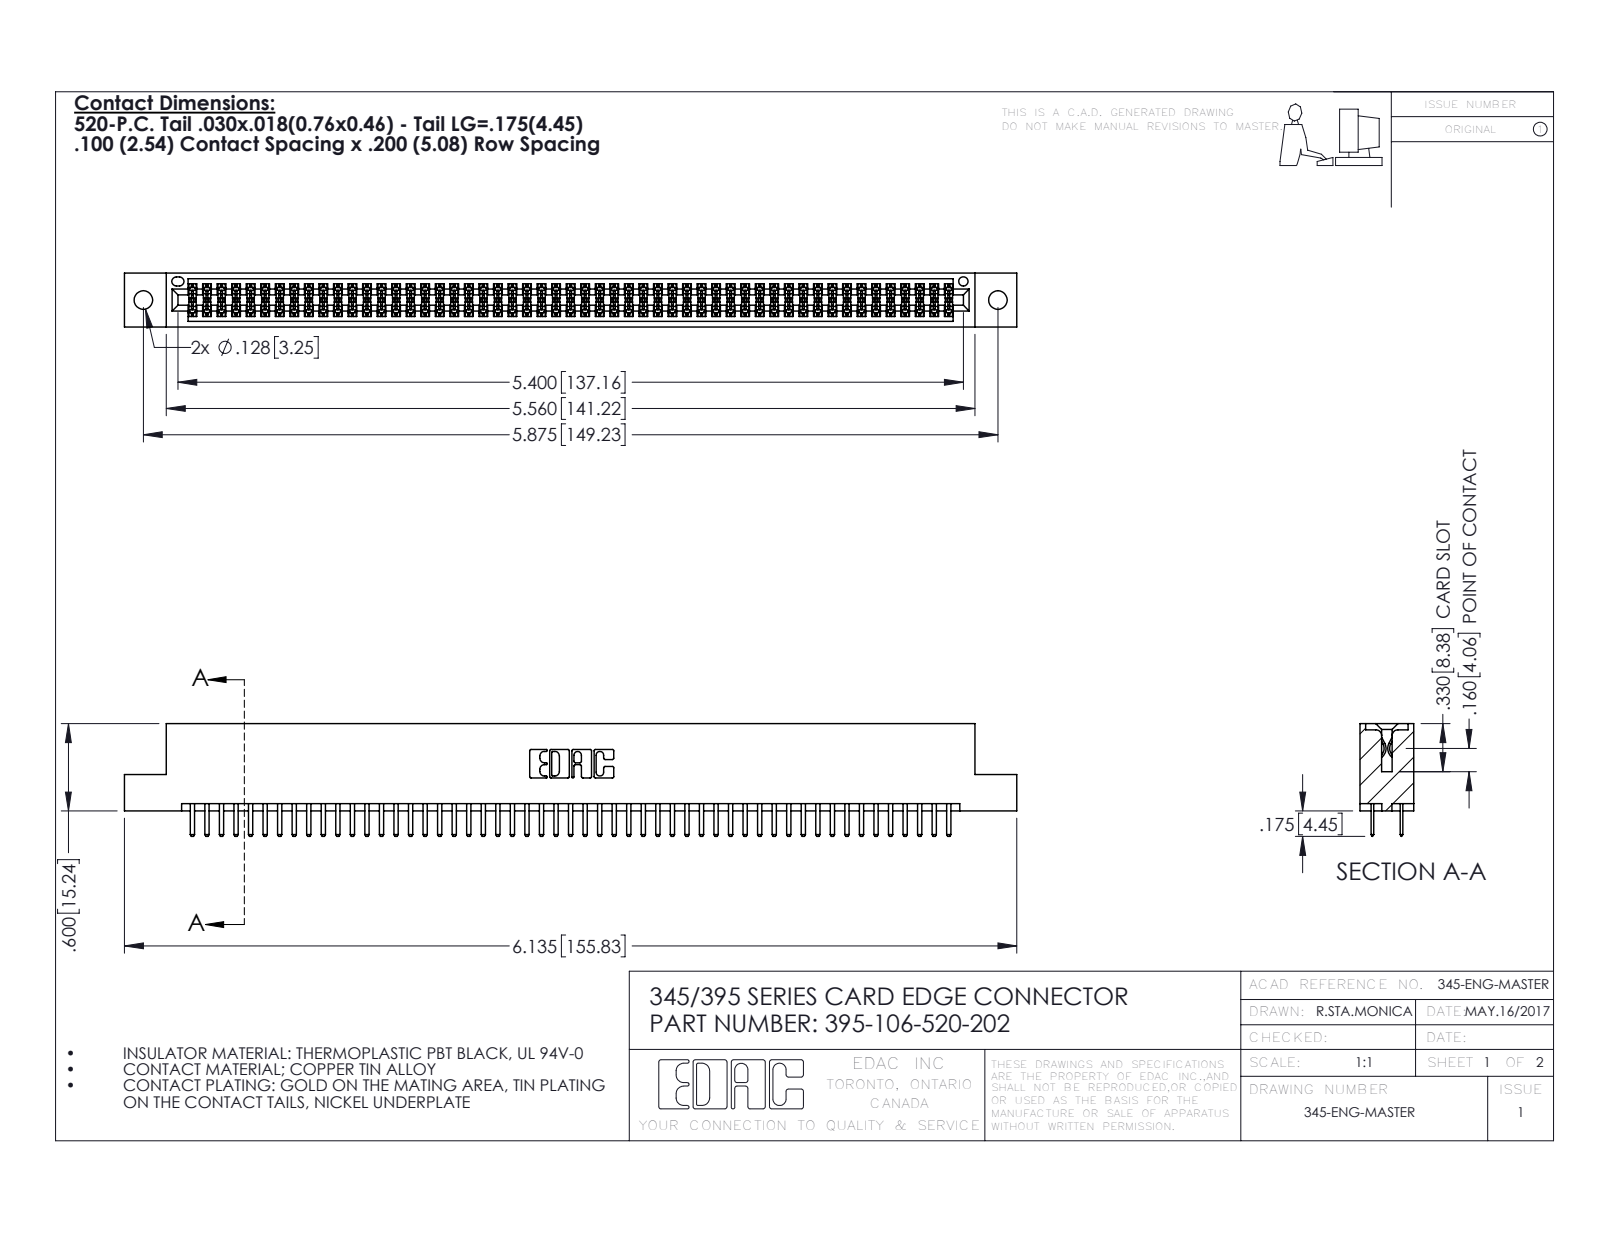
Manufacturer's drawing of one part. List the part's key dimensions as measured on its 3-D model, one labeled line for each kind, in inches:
Part name (STEP PRODUCT): 345 Part_Flush Mounting Lugs - 0.128 Dia; 345-292-001_345-293-120; 395-106-520-202
STEP written by: SolidWorks 2016 (CONFIG_CONTROL_DESIGN)
Units: inches
Bodies: 107 solids, 5850 faces (3790 planar, 2060 cylindrical, 0 other)
Overall size (bounding box): 6.135 × 0.775 × 0.37
Volume: 0.925 in³ · Surface area: 34.48 in²
Round holes (diameter × count): ⌀0.128 ×2, ⌀0.064 ×1
Partial cylindrical surfaces — rounded edges, fillets, slot ends (radius × count): R0.006 ×159, R0.01 ×110, R0.01 ×22, R0.007 ×6, R0.031 ×6, R0.026 ×3, R0.014 ×2, R0.019 ×2
Main face-to-face distances: 0.298, 0.072, 0.2, 0.37, 0.098, 0.272, 0.025, 0.225, 0.022, 0.072
Hole centre spacings: 0.27, 5.639, 5.875
